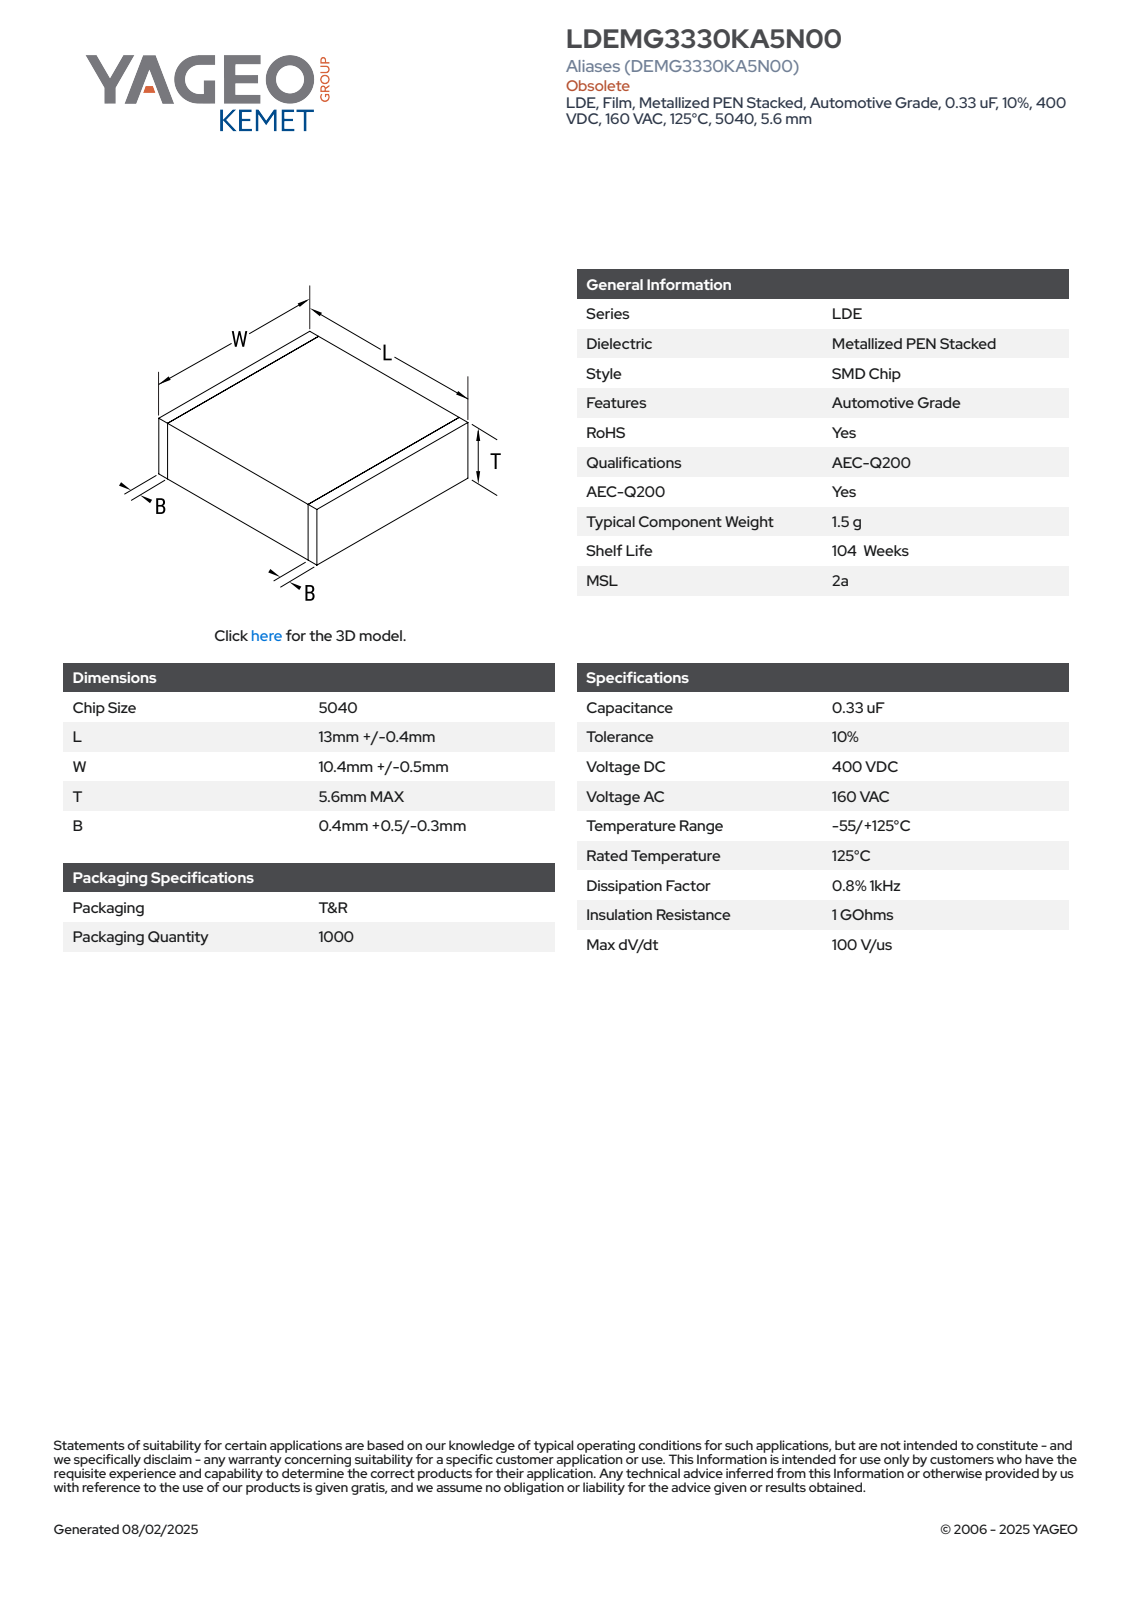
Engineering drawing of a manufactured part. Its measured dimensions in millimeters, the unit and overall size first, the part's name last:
Units: millimetres
Overall size (bounding box): 13.4 × 10.9 × 5.6
Main face-to-face distances: 5.58, 10.88, 13.4, 5.59, 10.89, 5.6, 10.9, 0.5, 12.9, 12.4
Volume: 814 mm³ · Surface area: 573 mm²
Bodies: 4 solids, 73 faces (73 planar, 0 cylindrical, 0 other)
Part name (STEP PRODUCT): CFS_LDELDB_5040_L13.4W10.9T5.6B0.9
STEP written by: SolidWorks 2020 (AUTOMOTIVE_DESIGN)
